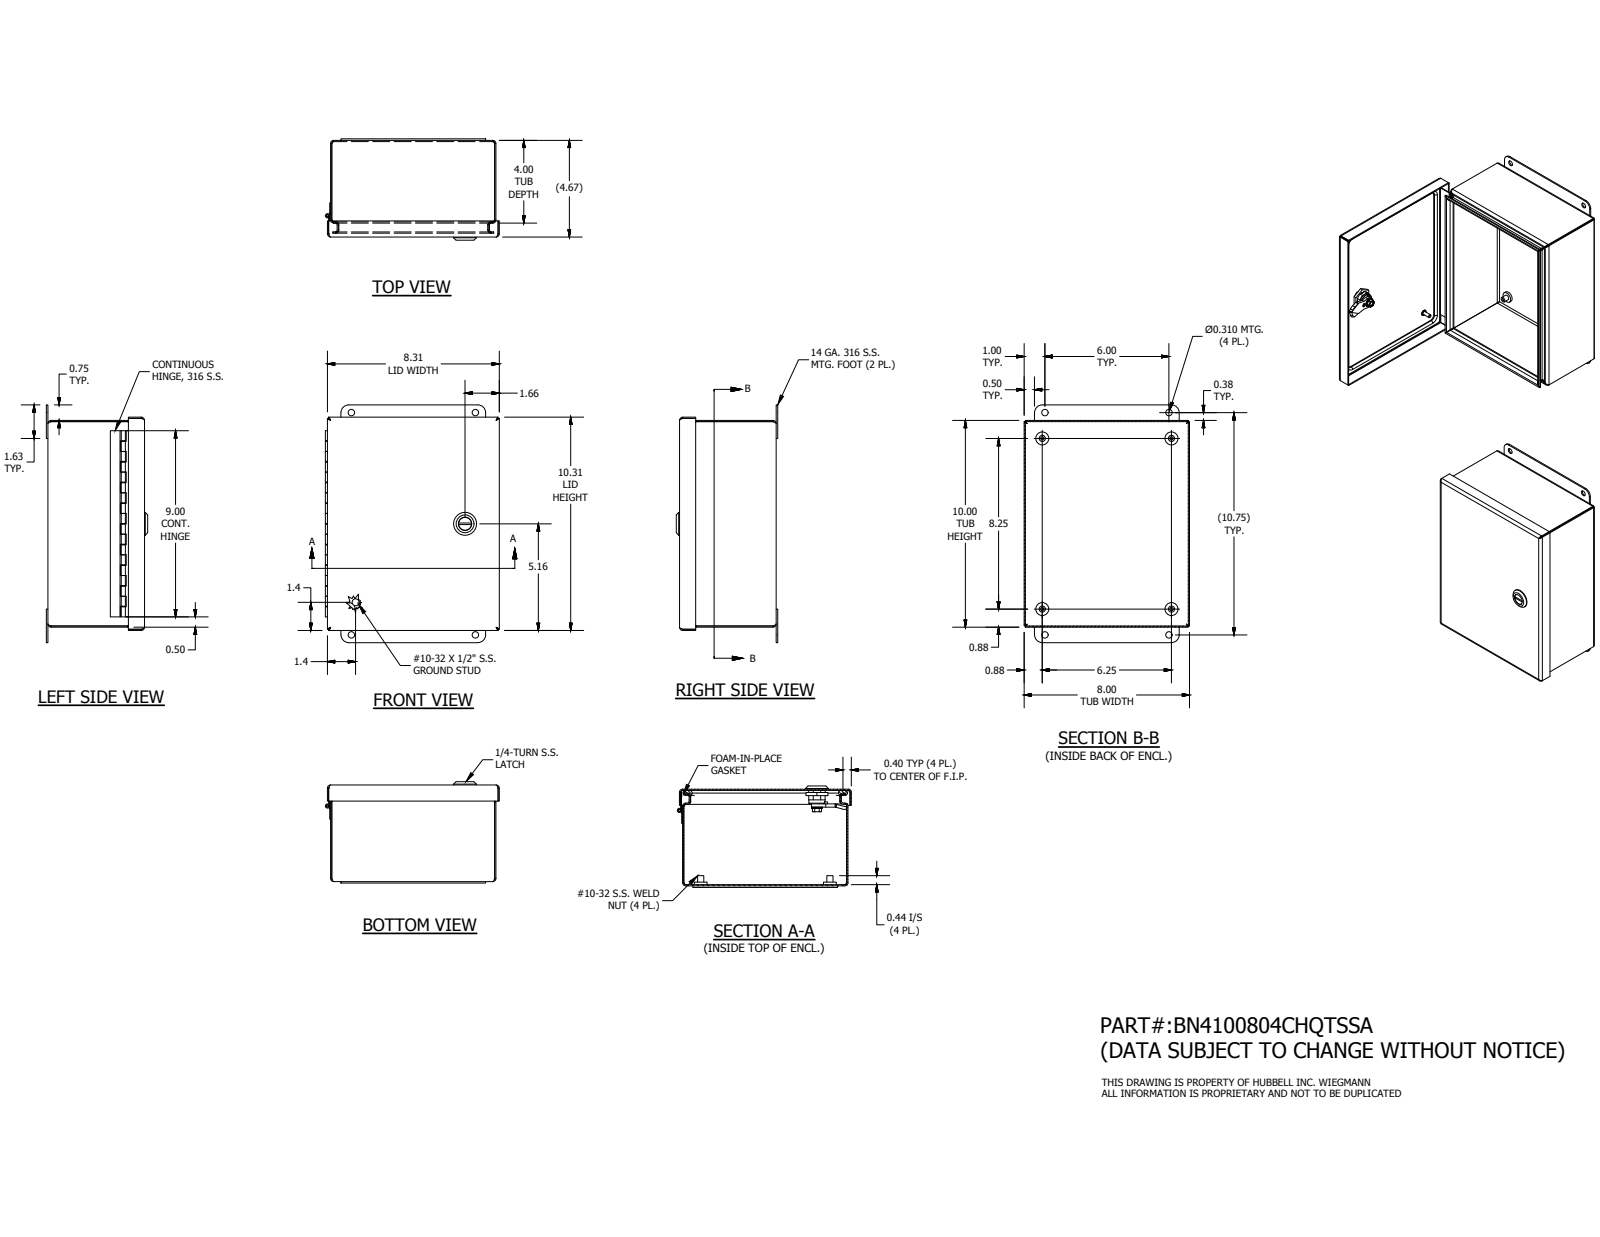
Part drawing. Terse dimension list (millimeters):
name: BN41008CHQTSSALID; 10x8; 348129; 32883LH (+8 more)
written by: Autodesk Inventor 2016 (AUTOMOTIVE_DESIGN)
unit: mm
bodies: 21 solids, 651 faces (354 planar, 200 cylindrical, 97 other)
size: 292.1 × 213.66 × 124.59
volume: 451 279 mm³; area: 557 422 mm²
holes: 4× ⌀3.96, 4× ⌀7.87, 1× ⌀2.96, 1× ⌀5, 1× ⌀8, 1× ⌀10, 1× ⌀10.2, 1× ⌀16.1, 1× ⌀20.38
bosses: 4× ⌀15.88, 4× ⌀7.62, 1× ⌀28, 1× ⌀19.8, 1× ⌀16, 1× ⌀15.2, 1× ⌀13.5, 1× ⌀12.8
rounds: 20× R2.38, 20× R3.88, 16× R3.17, 8× R0.5, 4× R4, 4× R9.53, 2× R2.31, 1× R6.45
face distances: 1.5, 1.49, 117.19, 118.68, 115.69, 117.18, 252.5, 201.71, 203.2, 200.21
hole spacings: 31.91, 241.32, 152.4, 158.75, 158.78, 158.79, 177.17, 209.55
